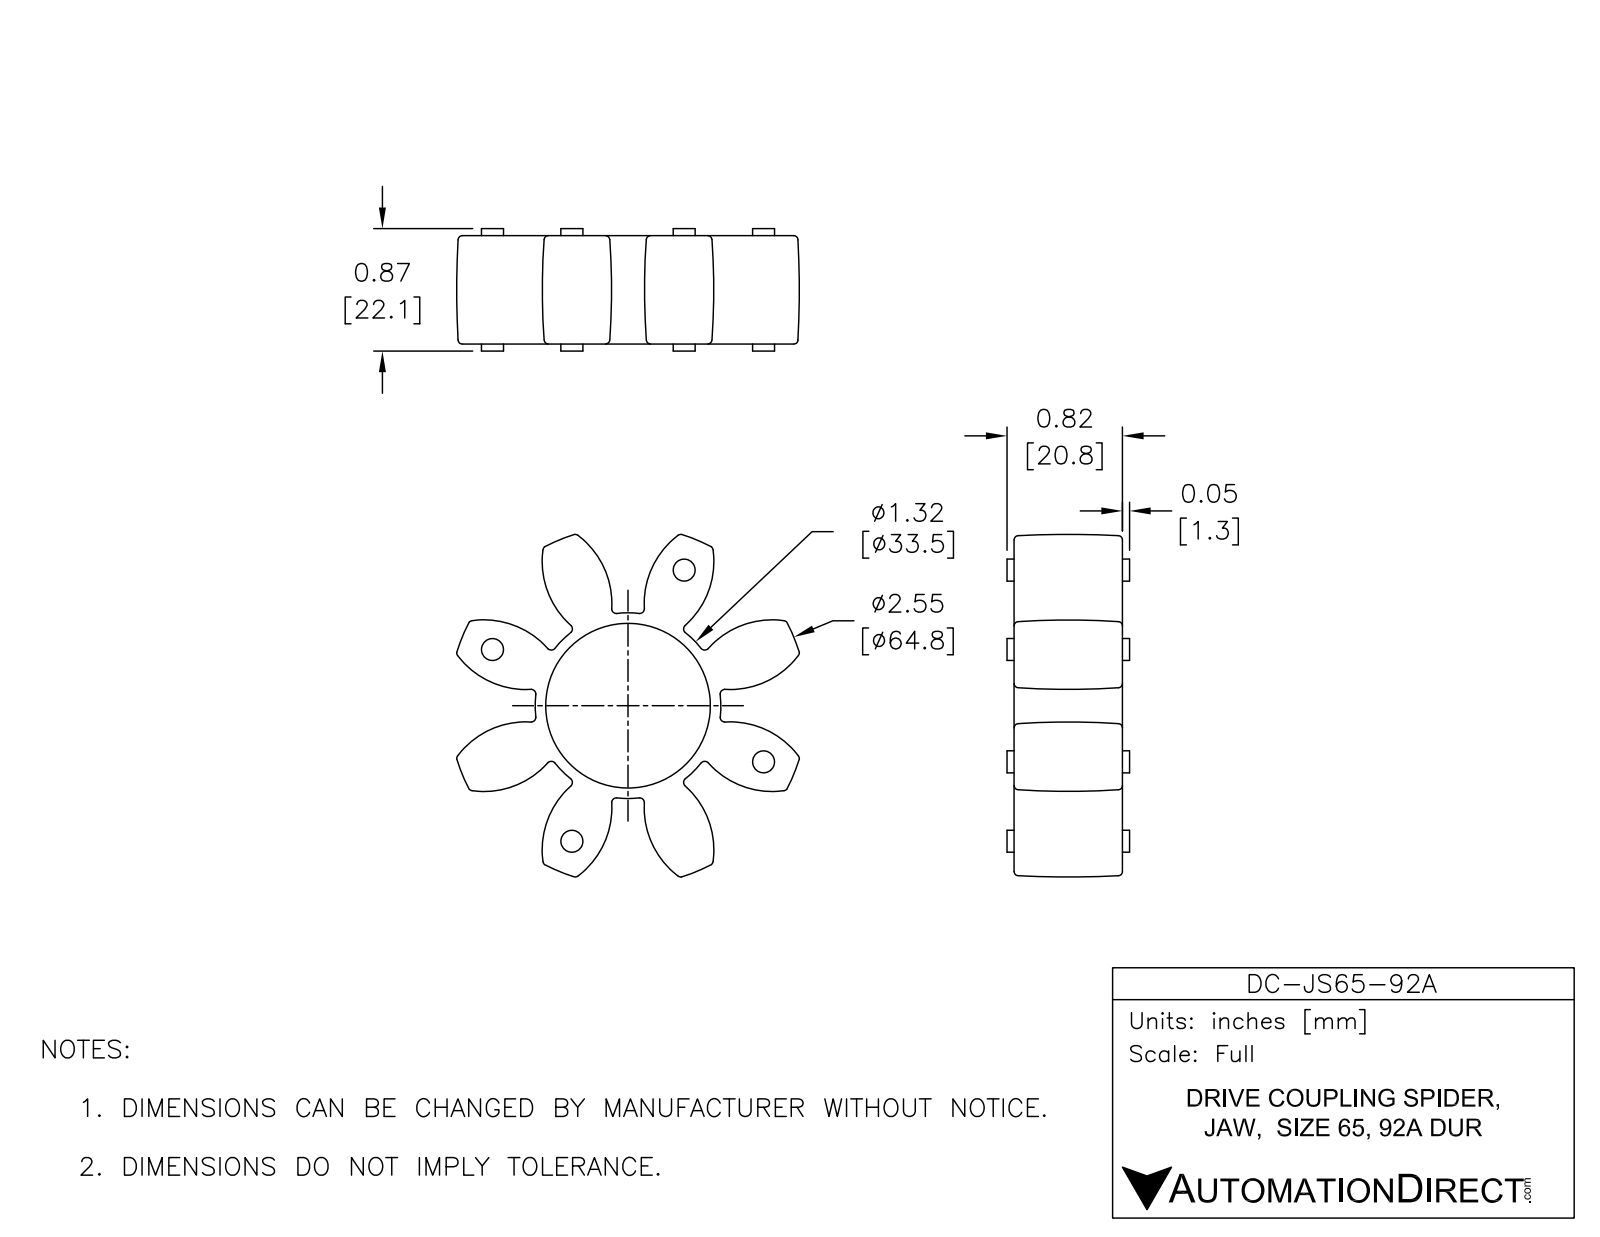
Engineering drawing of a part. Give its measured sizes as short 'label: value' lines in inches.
name: DC-JS65-92A
written by: SolidWorks 2015 (AUTOMOTIVE_DESIGN)
unit: in
bodies: 1 solid, 264 faces (10 planar, 58 cylindrical, 196 other)
size: 2.413 × 2.413 × 0.87
volume: 1.537 in³; area: 17.31 in²
holes: 1× ⌀1.17
bosses: 8× ⌀0.156
rounds: 32× R0.03
face distances: 0.77, 0.05, 0.82, 0.87
